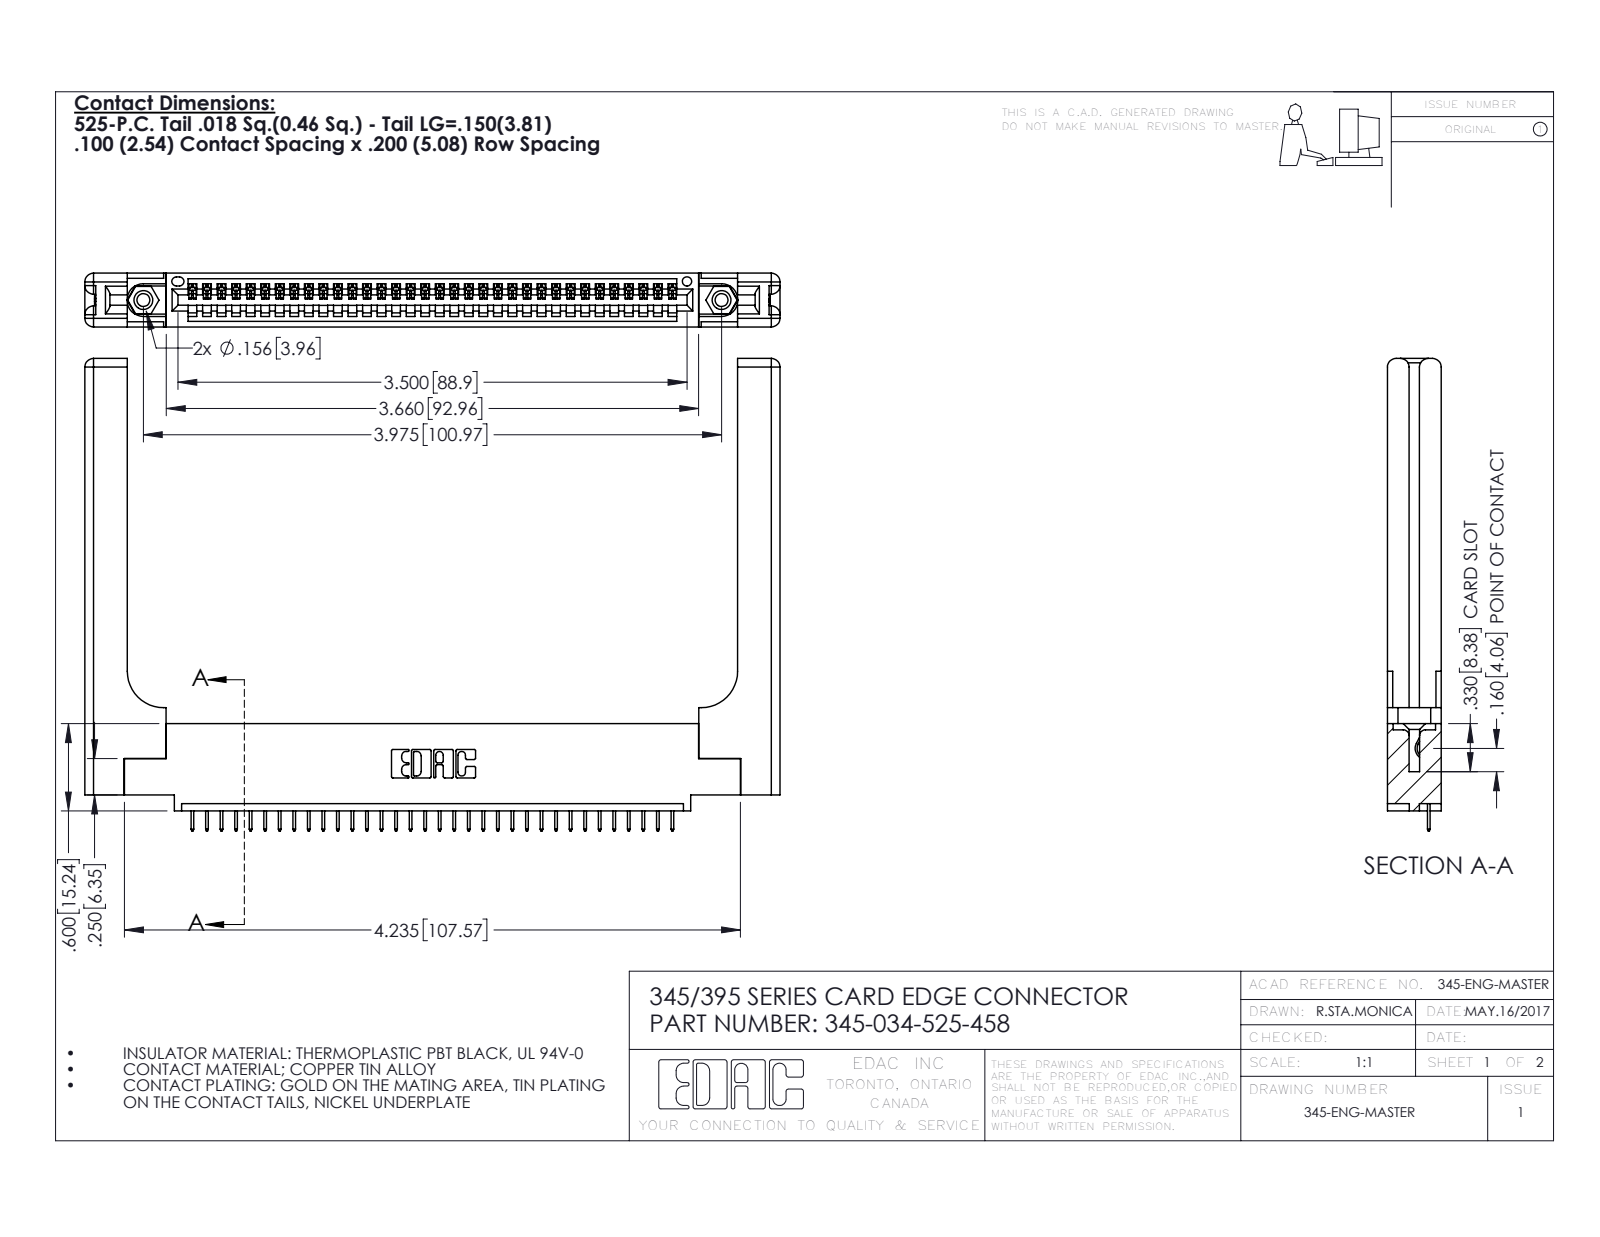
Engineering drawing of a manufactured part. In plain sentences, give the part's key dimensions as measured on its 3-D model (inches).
The part is named "345-250-001_345-250-001-102; 345 Part_0.110 Offset - 0.156 Dia-TH; 345-292-001_345-293-125; 345-034-525-458 (+1 more)". Its 3-D file was written by "SolidWorks 2020 (CONFIG_CONTROL_DESIGN)". It is 39 solids with 2494 faces: 1796 planar, 638 cylindrical and 60 other. Overall it measures 4.779 by 3.247 by 0.37 inches. Its volume is 1.206 cubic inches and its surface area 30.64 square inches. Round holes: 2 of diameter 0.089, 2 of diameter 0.125, 2 of diameter 0.156, 1 of diameter 0.064. Round bosses or shafts: 2 of diameter 0.155. Partial cylindrical surfaces (rounded edges, fillets, slot ends): 68 of radius 0.006, 22 of radius 0.01, 16 of radius 0.06, 6 of radius 0.007, 6 of radius 0.031, 3 of radius 0.026, 2 of radius 0.03, 2 of radius 0.031. The main face-to-face distances are 0.37, 0.072, 0.298, 0.2, 0.15, 0.148, 0.098, 0.272, 0.025, 0.077. The hole center spacings are 0.27, 3.74, 3.975.
